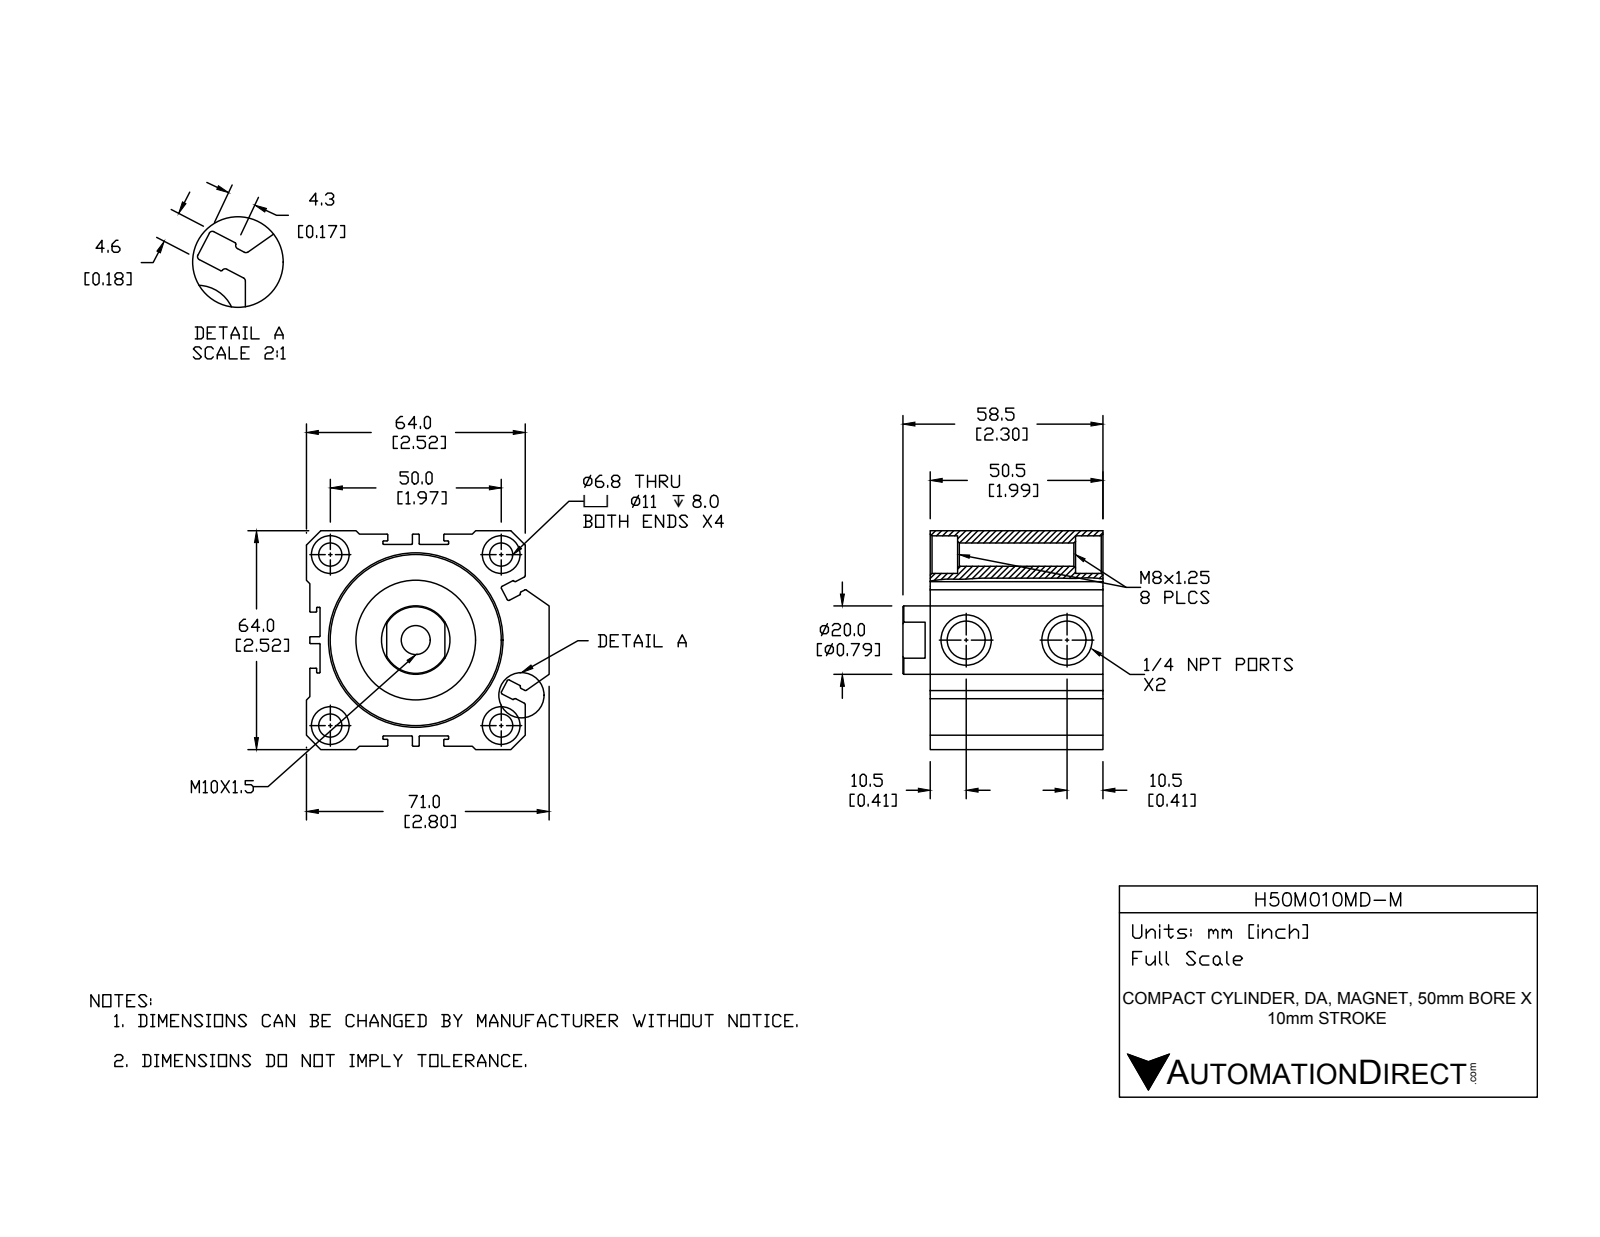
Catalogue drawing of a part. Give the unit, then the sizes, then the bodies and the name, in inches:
Units: inches
Overall size (bounding box): 2.795 × 2.52 × 2.303
Round holes (diameter × count): ⌀0.268 ×4, ⌀0.433 ×4, ⌀0.438 ×2, ⌀0.335 ×1, ⌀0.787 ×1, ⌀1.417 ×1, ⌀1.969 ×1
Round bosses / shafts (diameter × count): ⌀1.378 ×1, ⌀1.22 ×1
Partial cylindrical surfaces — rounded edges, fillets, slot ends (radius × count): R0.008 ×40, R0.02 ×12
Main face-to-face distances: 0.157, 0.039, 0.118, 2.48, 2.362, 1.22, 1.181, 0.276, 0.394, 0.079
Hole centre spacings: 1.392, 1.969, 2.784, 1.161
Volume: 9.625 in³ · Surface area: 78.19 in²
Bodies: 2 solids, 255 faces (99 planar, 103 cylindrical, 53 other)
Part name (STEP PRODUCT): H50M010MD-M; H50M010MD-M-PISTON; H50M010MD-M-BODY
STEP written by: SolidWorks 2015 (CONFIG_CONTROL_DESIGN)
